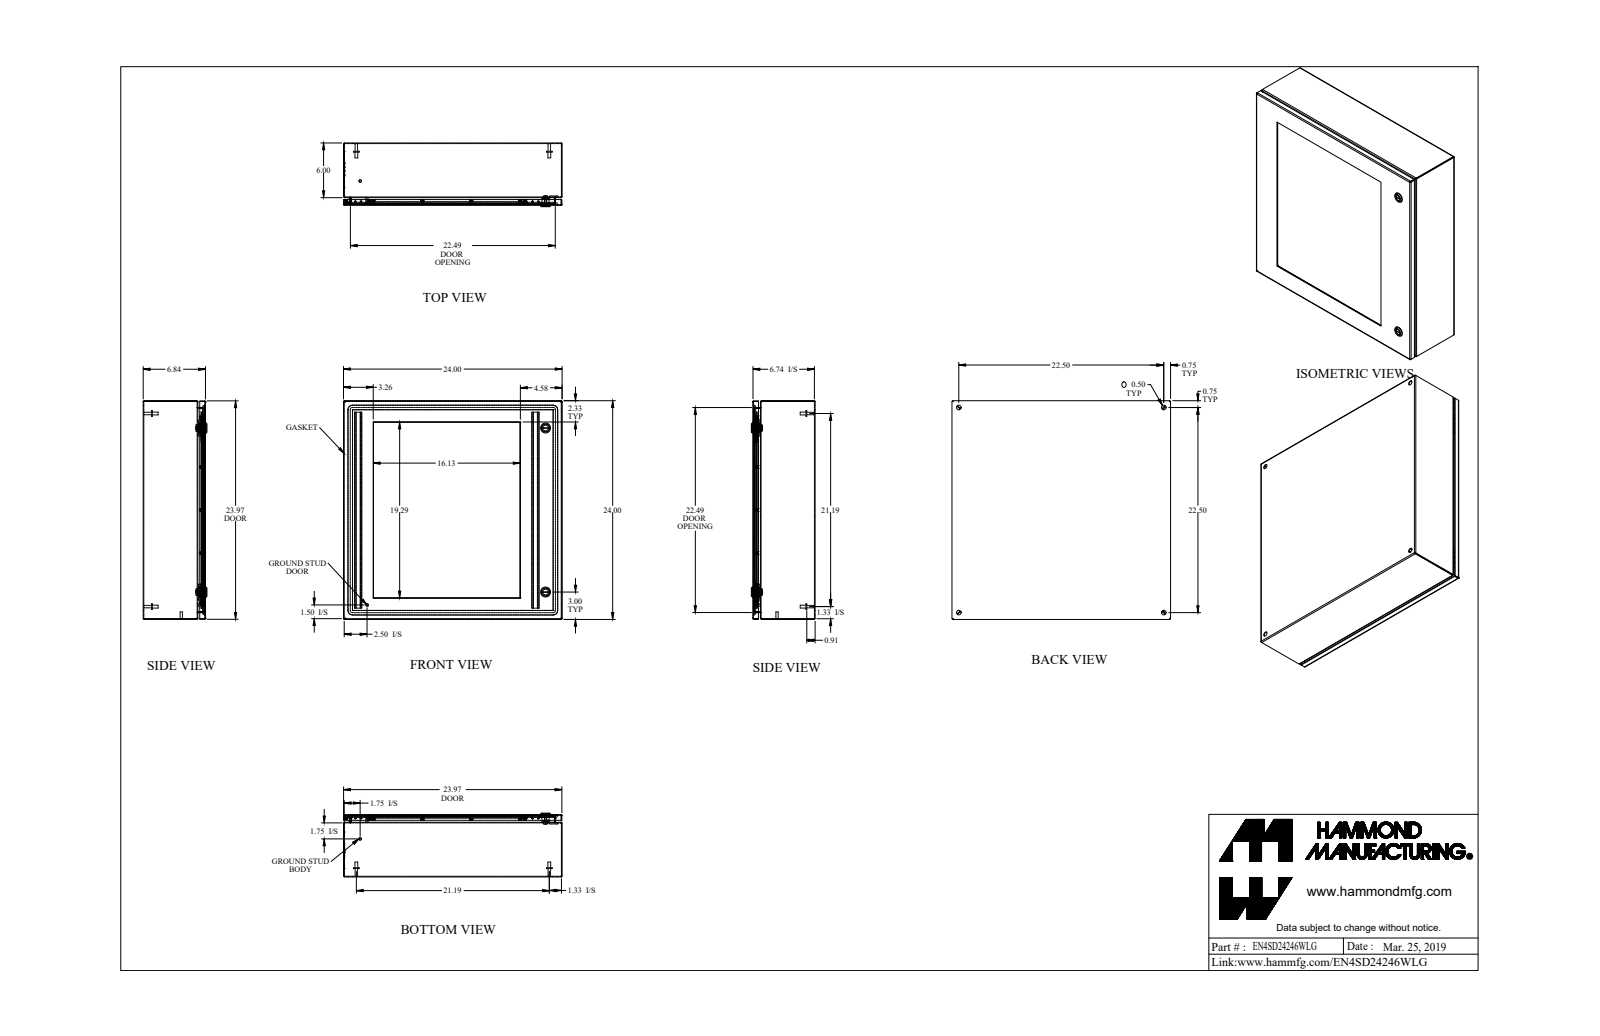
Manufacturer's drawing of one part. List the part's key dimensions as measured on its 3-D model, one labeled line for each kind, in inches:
Part name (STEP PRODUCT): EN4SD24246WLG_Default
STEP written by: SolidWorks 2019 (CONFIG_CONTROL_DESIGN)
Units: inches
Bodies: 72 solids, 1482 faces (763 planar, 453 cylindrical, 266 other)
Overall size (bounding box): 24 × 24 × 6.997
Volume: 217 in³ · Surface area: 4 501 in²
Round holes (diameter × count): ⌀0.13 ×18, ⌀0.25 ×18, ⌀0.5 ×4, ⌀0.232 ×2, ⌀0.625 ×2, ⌀0.785 ×2, ⌀0.172 ×1, ⌀0.24 ×1, ⌀0.242 ×1
Round bosses / shafts (diameter × count): ⌀0.226 ×19, ⌀0.368 ×18, ⌀0.164 ×18, ⌀0.625 ×4, ⌀0.313 ×4, ⌀0.27 ×4, ⌀1.1 ×2, ⌀0.525 ×2
Partial cylindrical surfaces — rounded edges, fillets, slot ends (radius × count): R0.036 ×20, R0.108 ×20, R0.043 ×12, R0.081 ×12, R0.125 ×12, R0.382 ×12, R19.003 ×8, R0.006 ×4
Main face-to-face distances: 0.072, 6.765, 6.693, 23.928, 6.443, 0.25, 6.515, 0.322, 23.856, 24
Hole centre spacings: 4.719, 17.781, 14.156, 18.875, 19.57, 21.03, 5.372, 5.372
